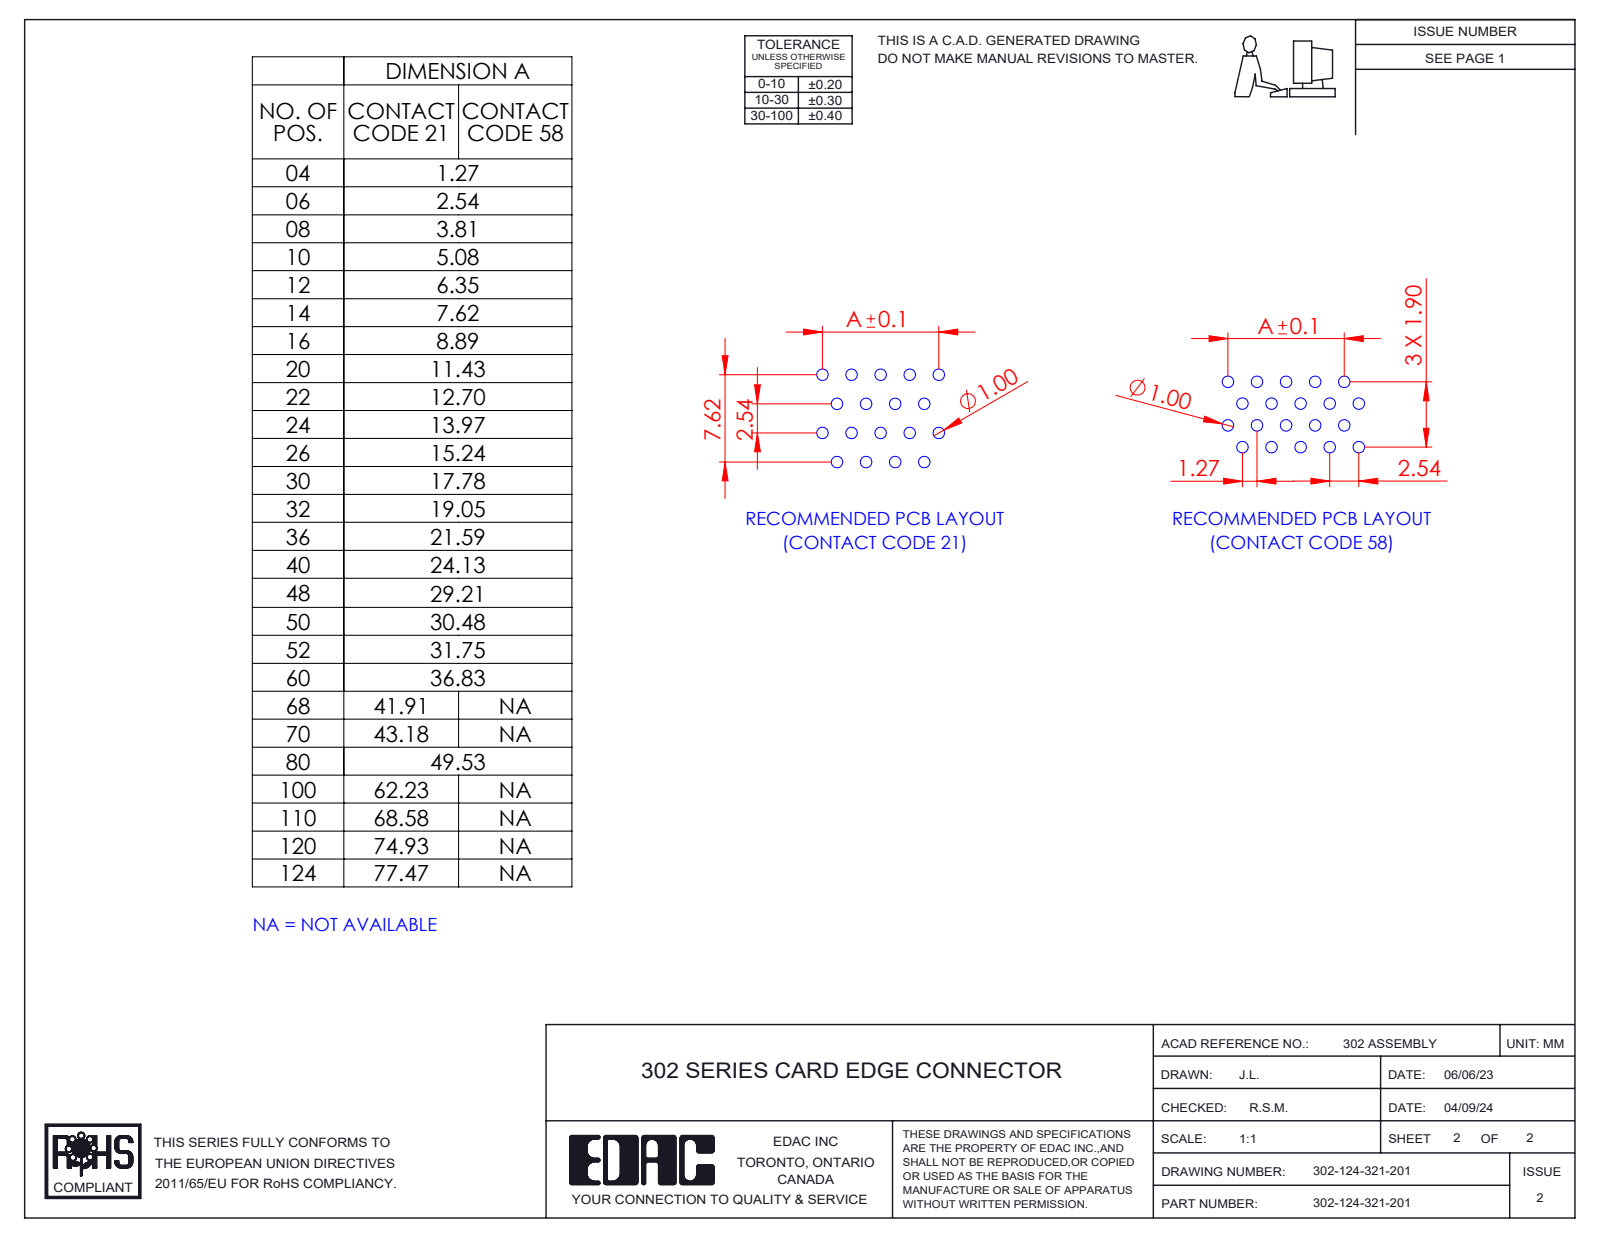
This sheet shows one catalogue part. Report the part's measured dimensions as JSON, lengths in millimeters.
{"part_name": "Contact_302-290-X21 (2); Contact_302-290-X21 (1); HSG_Vertical HSG; 302-124-321-201", "step_written_by": "SolidWorks 2023 (CONFIG_CONTROL_DESIGN)", "units": "millimeters", "bodies": {"solids": 125, "faces": 5708, "planar": 4203, "cylindrical": 1253, "other": 252}, "overall_size": [84.84, 17.63, 8.88], "volume_mm3": 6440, "surface_area_mm2": 18527, "partial_cylinders_radius": [[0.2, 132], [2.03, 4], [2.09, 4], [0.11, 2], [0.4, 2], [0.41, 2], [1.25, 2], [1.53, 2]], "face_to_face_distances": [8.88, 2.54, 1.27, 5.08, 3.81, 0.8, 0.47, 3.49, 5.39, 1.9]}
